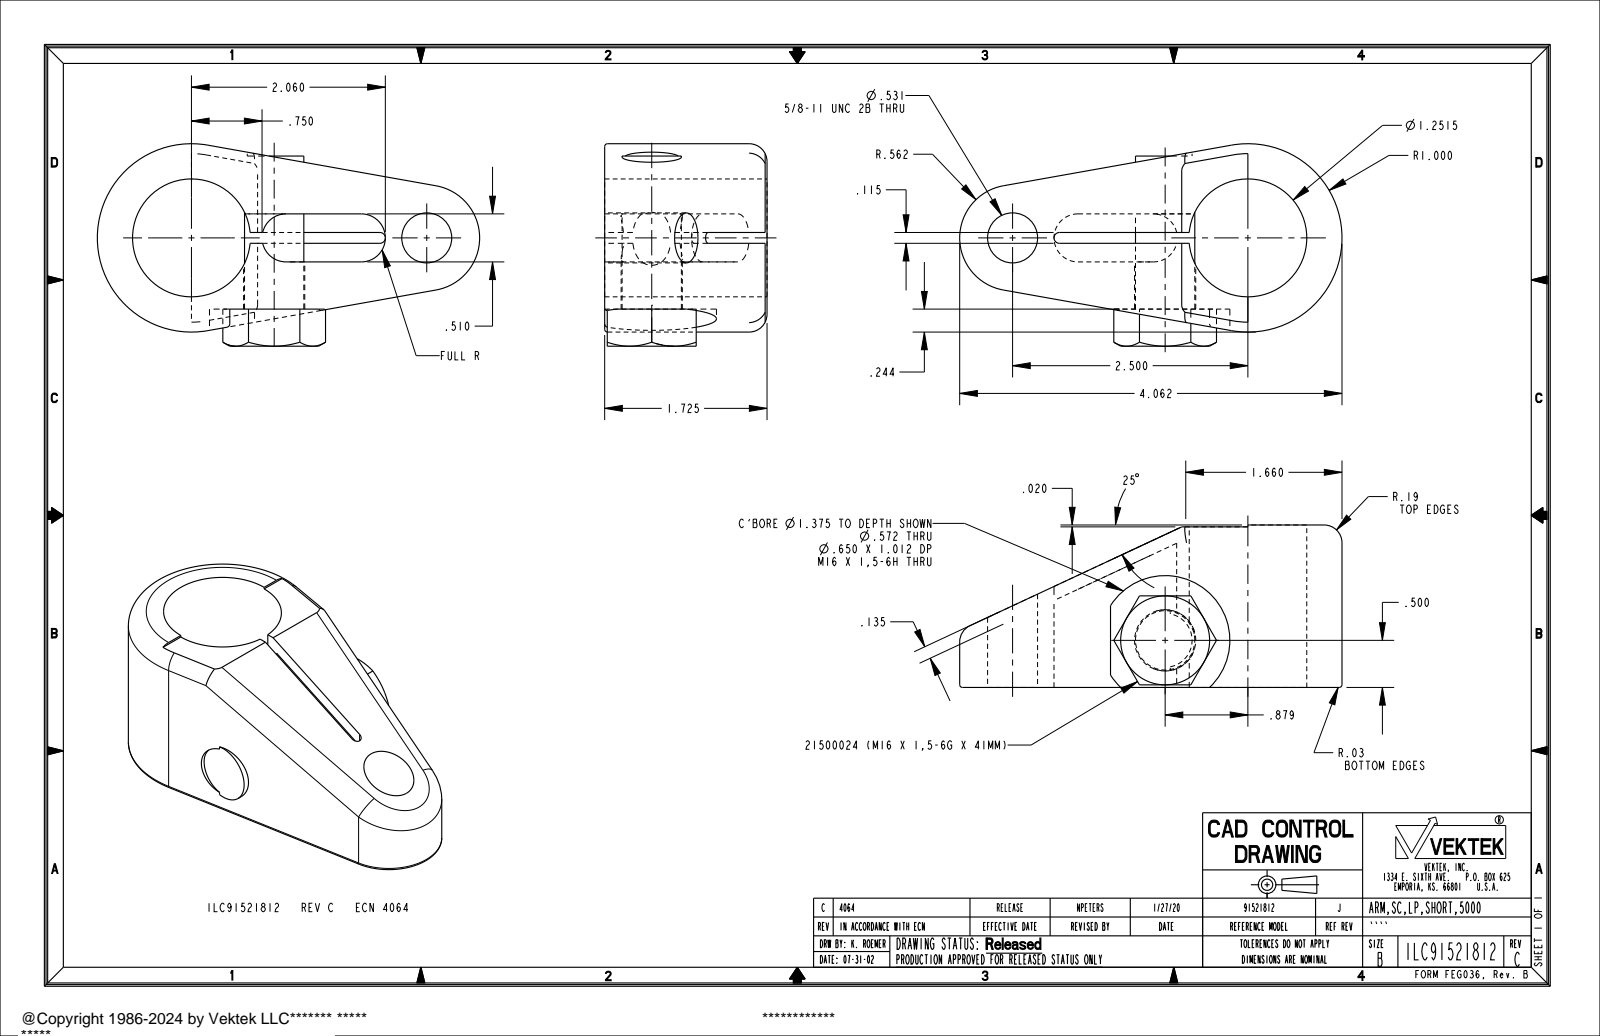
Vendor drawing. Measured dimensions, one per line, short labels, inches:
name: ILC91521812
written by: PRO/ENGINEER BY PARAMETRIC TECHNOLOGY CORPORATION, 2013320 (AUTOMOTIVE_DESIGN)
unit: in
bodies: 1 solid, 65 faces (27 planar, 28 cylindrical, 10 other)
size: 4.062 × 2.15 × 1.725
volume: 5.927 in³; area: 38.65 in²
holes: 1× ⌀0.531, 1× ⌀0.65, 1× ⌀1.251
bosses: 1× ⌀0.63
rounds: 4× R0.19, 2× R0.03, 2× R0.255, 1× R0.057, 1× R0.286, 1× R0.562, 1× R0.687, 1× R1
face distances: 0.51, 0.895, 1.405, 0.198, 0.313, 1.705, 0.394, 0.501, 1.011, 0.134
hole spacings: 2.5
